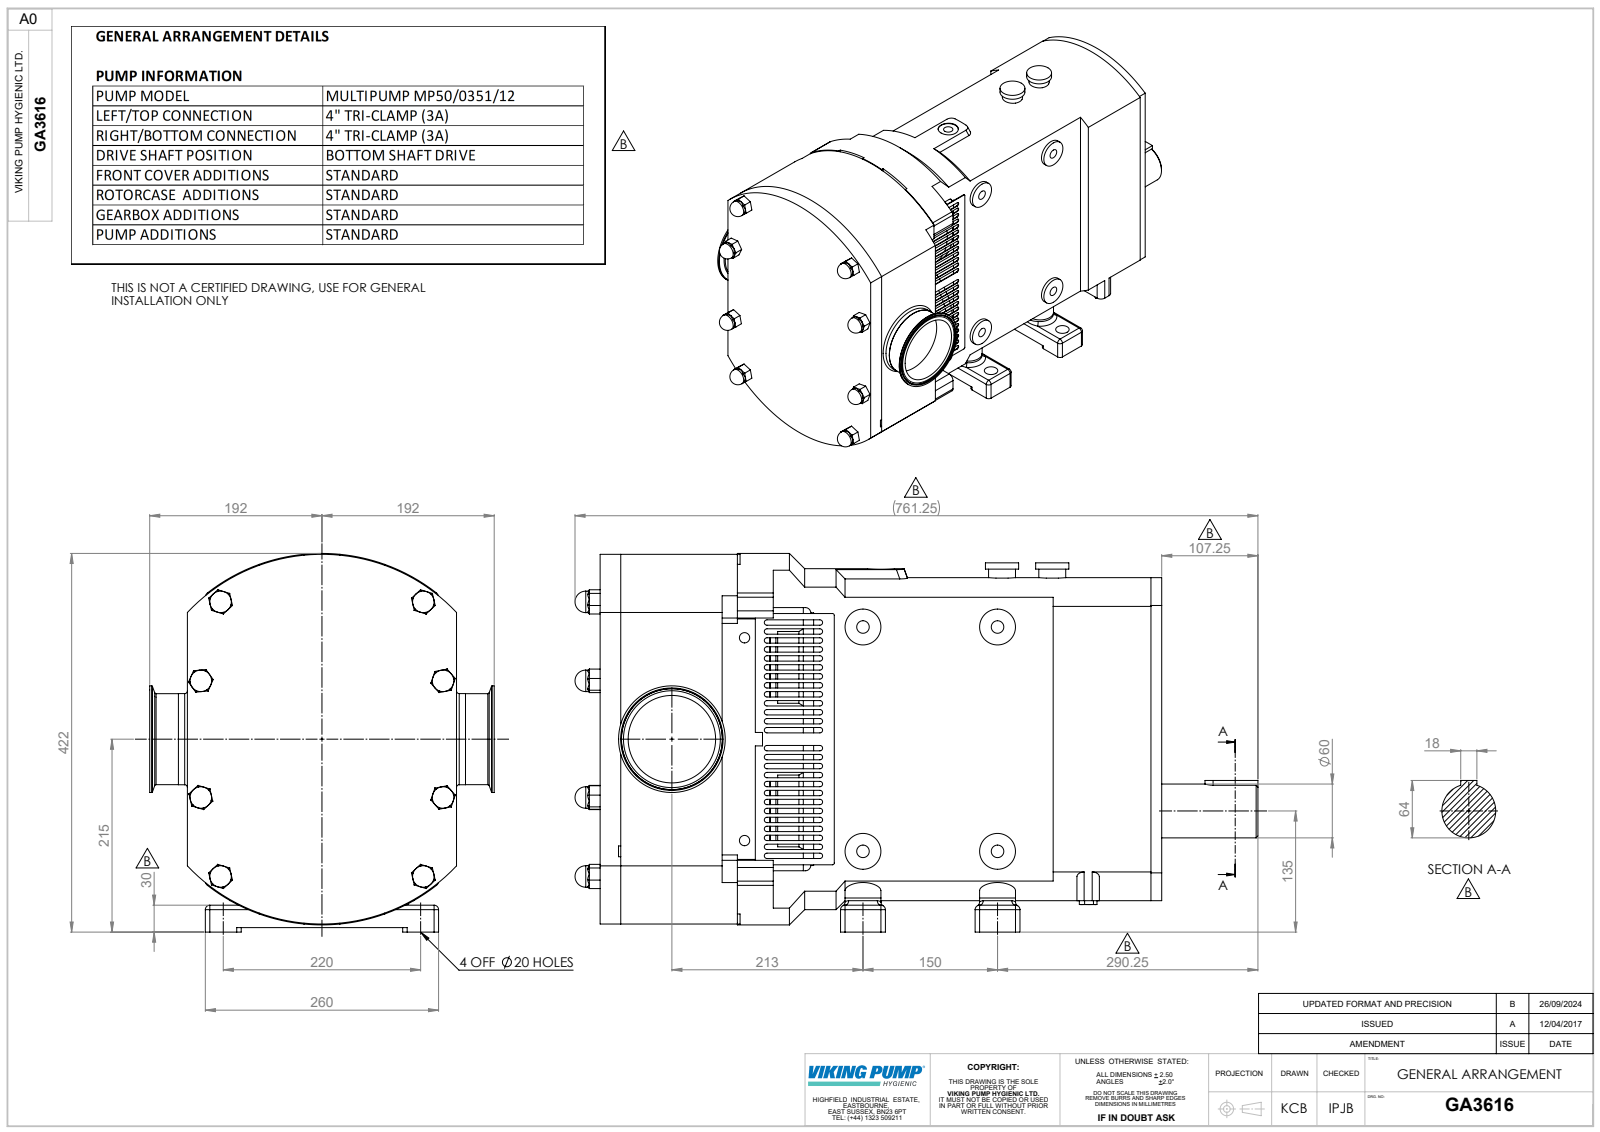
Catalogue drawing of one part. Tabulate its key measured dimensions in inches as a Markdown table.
| quantity | value |
| --- | --- |
| part name | Copy of Z94-5121-66 - 4 INCH^GA3616; GA3616; Copy of CP50S-0351 H BSD^GA3616 |
| STEP written by | SolidWorks 2023 (AUTOMOTIVE_DESIGN) |
| units | inches |
| bodies | 3 solids, 1132 faces (488 planar, 371 cylindrical, 273 other) |
| overall size | 29.97 × 16.614 × 15.118 |
| volume | 2 770 in³ |
| surface area | 2 074 in² |
| round holes (diameter × count) | 0.551 × 4, 0.787 × 4, 0.453 × 2, 1.378 × 2, 0.545 × 1, 1.181 × 1, 3.839 × 1 |
| round bosses / shafts (diameter × count) | 1.575 × 8, 0.945 × 8, 6.654 × 2, 3.15 × 2, 2.756 × 2, 2.677 × 2, 1.457 × 2, 1.25 × 2 |
| partial cylindrical surfaces (radius × count) | 0.118 × 52, 0.197 × 36, 0.236 × 14, 0.315 × 12, 0.079 × 4, 0.354 × 1, 6.083 × 1, 6.496 × 1 |
| main face-to-face distances | 6.772, 24.646, 7.421, 0.65, 1.87, 2.52, 9.291, 9.941, 5.354, 1.772 |
| hole center spacings | 5.906, 4.335, 4.402, 4.952, 5.218, 5.474, 6.704, 7.483 |
